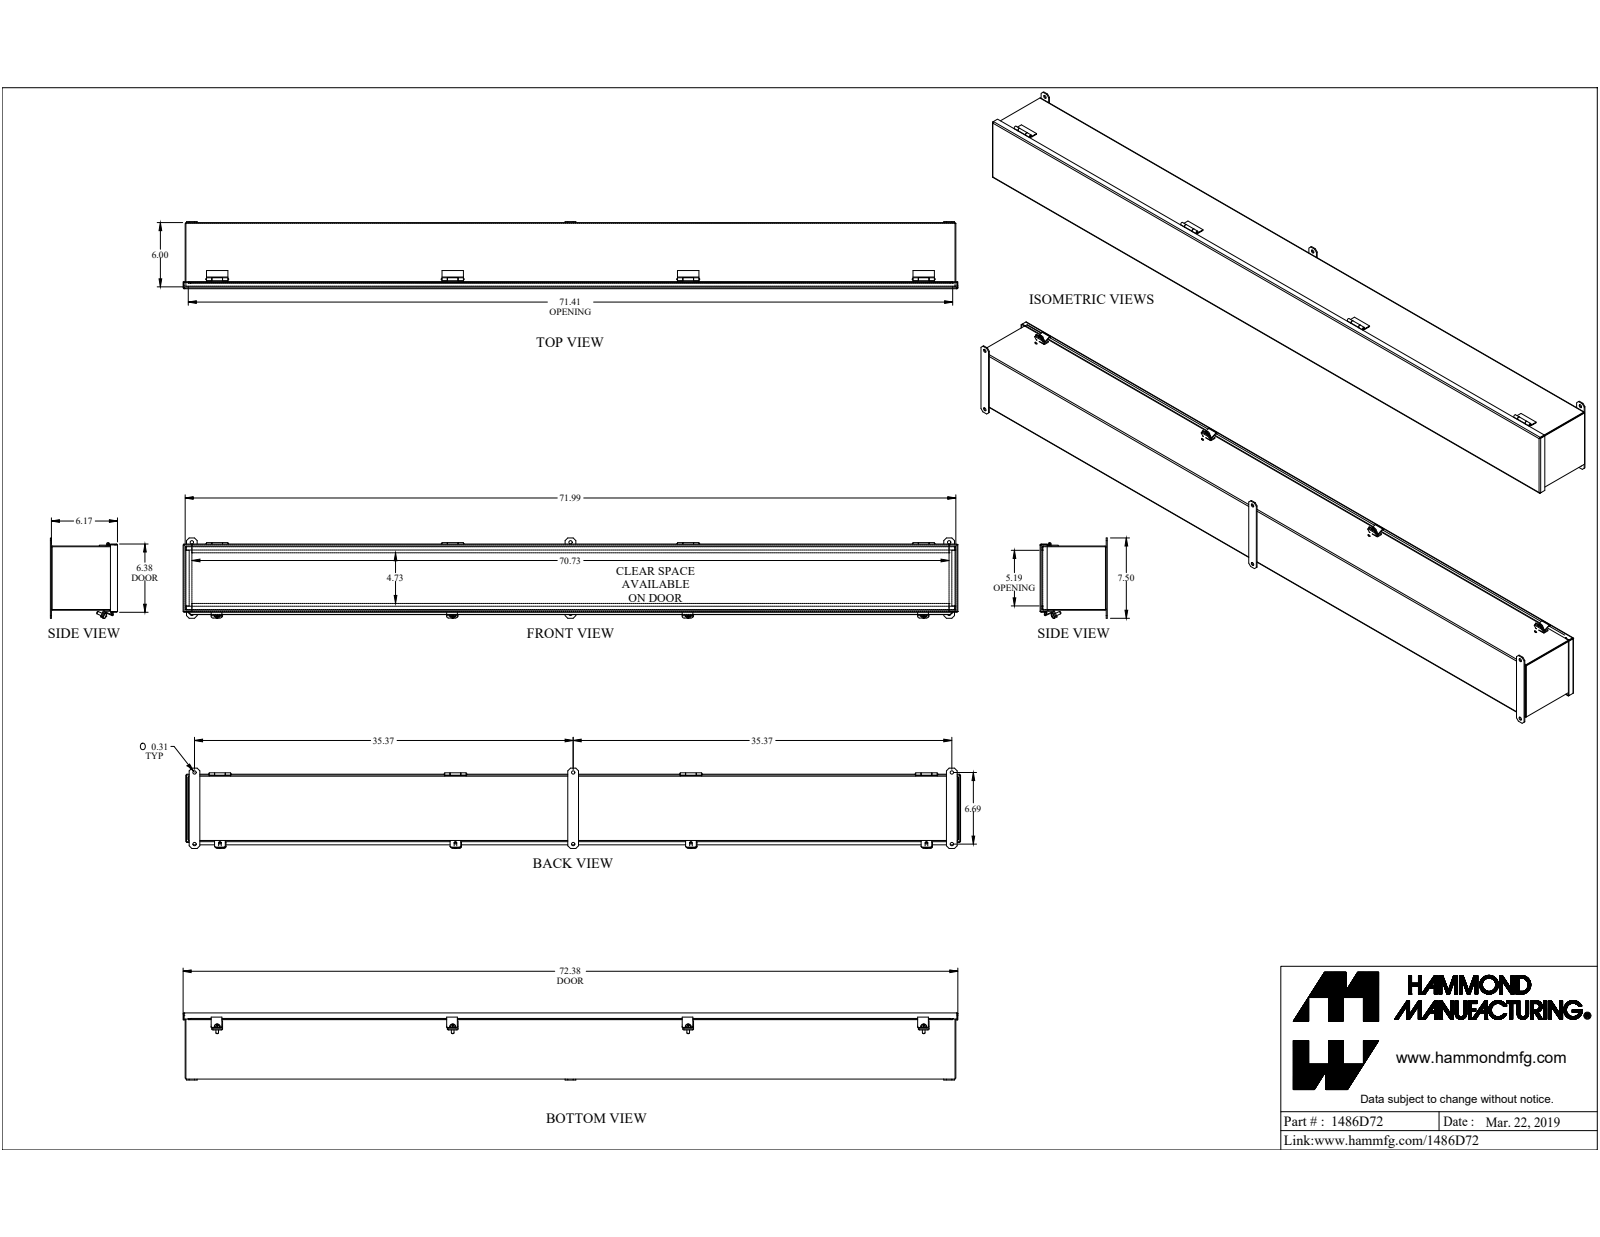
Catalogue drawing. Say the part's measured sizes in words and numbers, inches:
The part is named "1486D72". Its 3-D file was written by "SolidWorks 2019 (CONFIG_CONTROL_DESIGN)". It is 35 solids with 628 faces: 442 planar, 132 cylindrical and 54 other. Overall it measures 72.375 by 7.506 by 6.267 inches. Its volume is 166.3 cubic inches and its surface area 4 333 square inches. Round holes: 6 of diameter 0.313, 4 of diameter 0.213, 1 of diameter 0.125. Round bosses or shafts: 4 of diameter 0.48, 4 of diameter 0.246, 1 of diameter 0.275, 1 of diameter 0.125. Partial cylindrical surfaces (rounded edges, fillets, slot ends): 16 of radius 0.188, 11 of radius 0.036, 11 of radius 0.108, 8 of radius 0.01, 8 of radius 0.141, 2 of radius 0.029, 2 of radius 0.086, 1 of radius 0.048. The main face-to-face distances are 0.072, 5.928, 6.1, 6, 5.856, 6.172, 6.028, 5.913, 5.841, 0.187. The hole center spacings are 35.372, 35.999, 6.688, 22, 44, 70.744, 71.059, 66.
